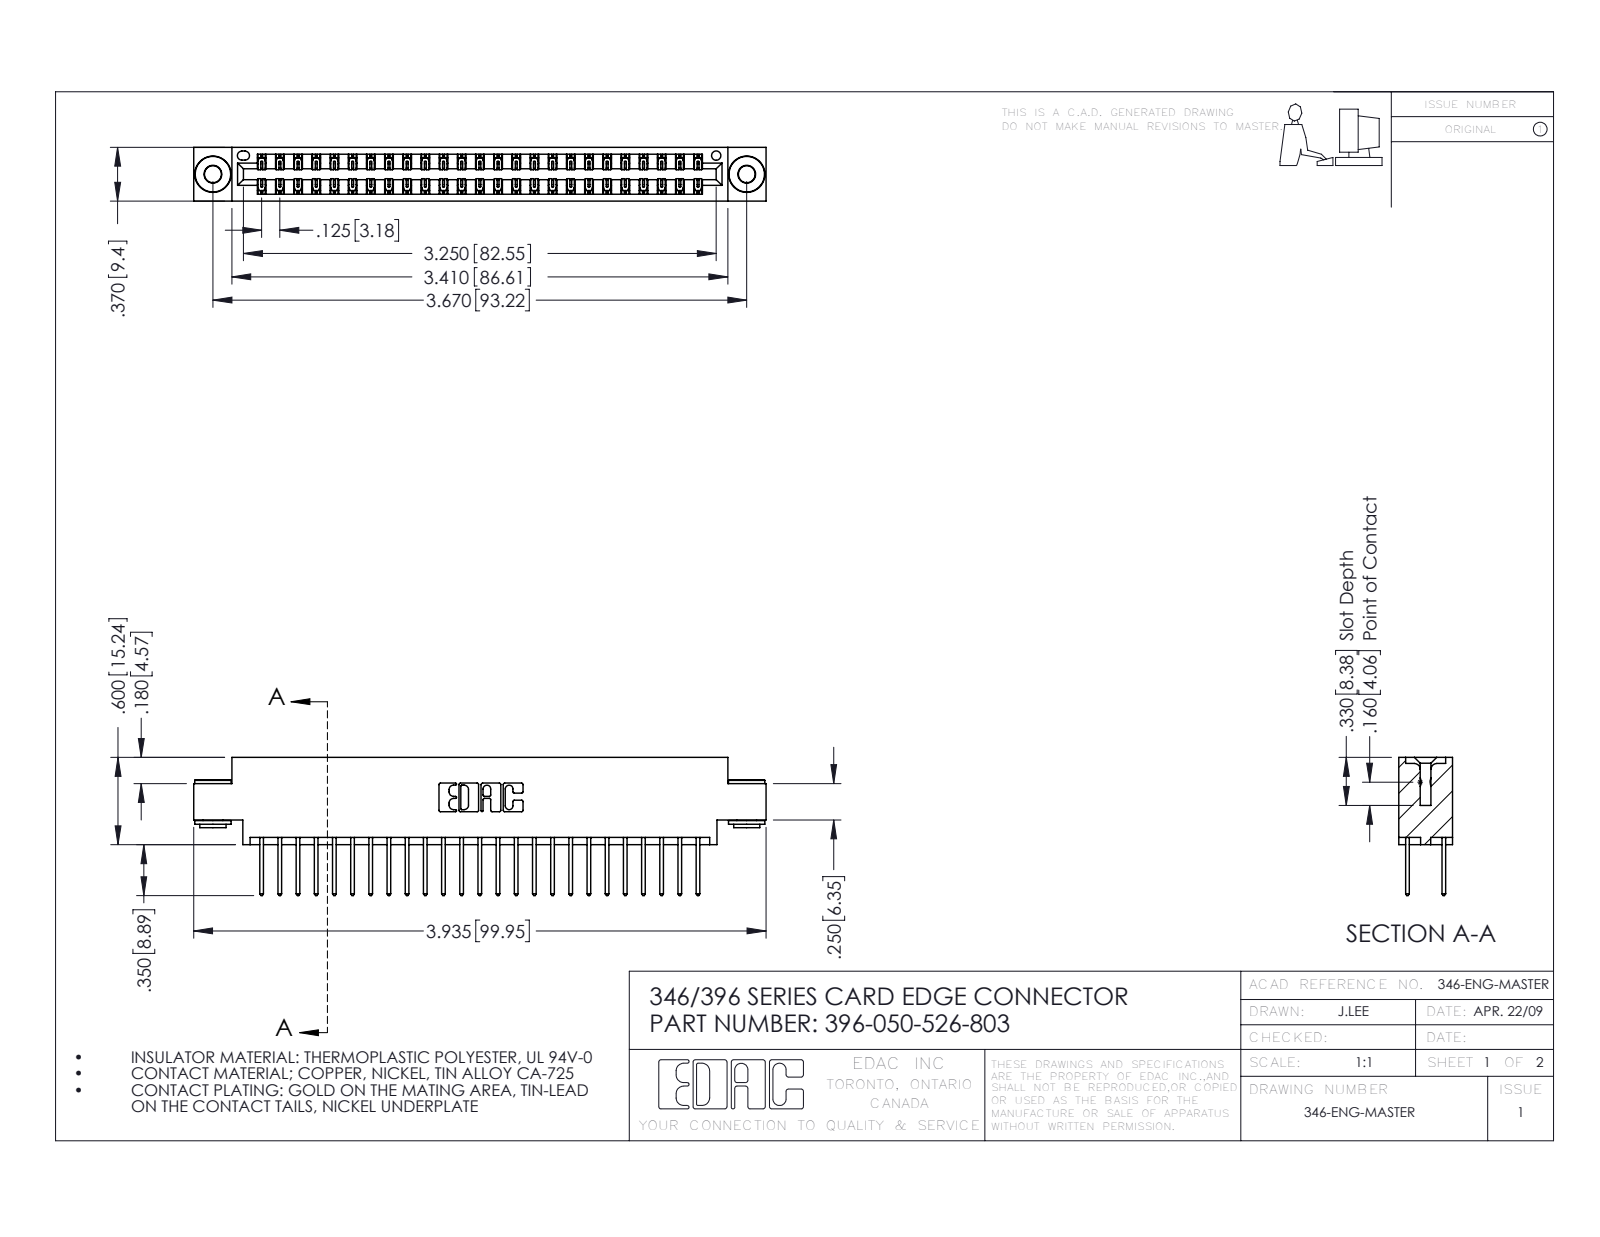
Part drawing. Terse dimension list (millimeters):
name: 345-250-002_345-250-002-102; 346 Part_0.170 Offset - 0.156 Dia-TH; 345-292-001_345-293-126; 396-050-526-803
written by: SolidWorks 2016 (CONFIG_CONTROL_DESIGN)
unit: mm
bodies: 53 solids, 2764 faces (1840 planar, 916 cylindrical, 8 other)
size: 99.9 × 24.1 × 9.4
volume: 9 550 mm³; area: 13 640 mm²
holes: 2× ⌀2.9, 2× ⌀4, 1× ⌀1.6
bosses: 2× ⌀6.4, 2× ⌀4.6, 2× ⌀3.5
rounds: 75× R0.2, 50× R0.3, 22× R0.3, 6× R0.2, 6× R0.8, 3× R0.7, 2× R0.4, 2× R0.6
face distances: 1.2, 8.2, 6.4, 9.4, 0.6, 1.8, 7.6, 7, 3.8, 5.6
hole spacings: 6.2, 87.9, 93.2
